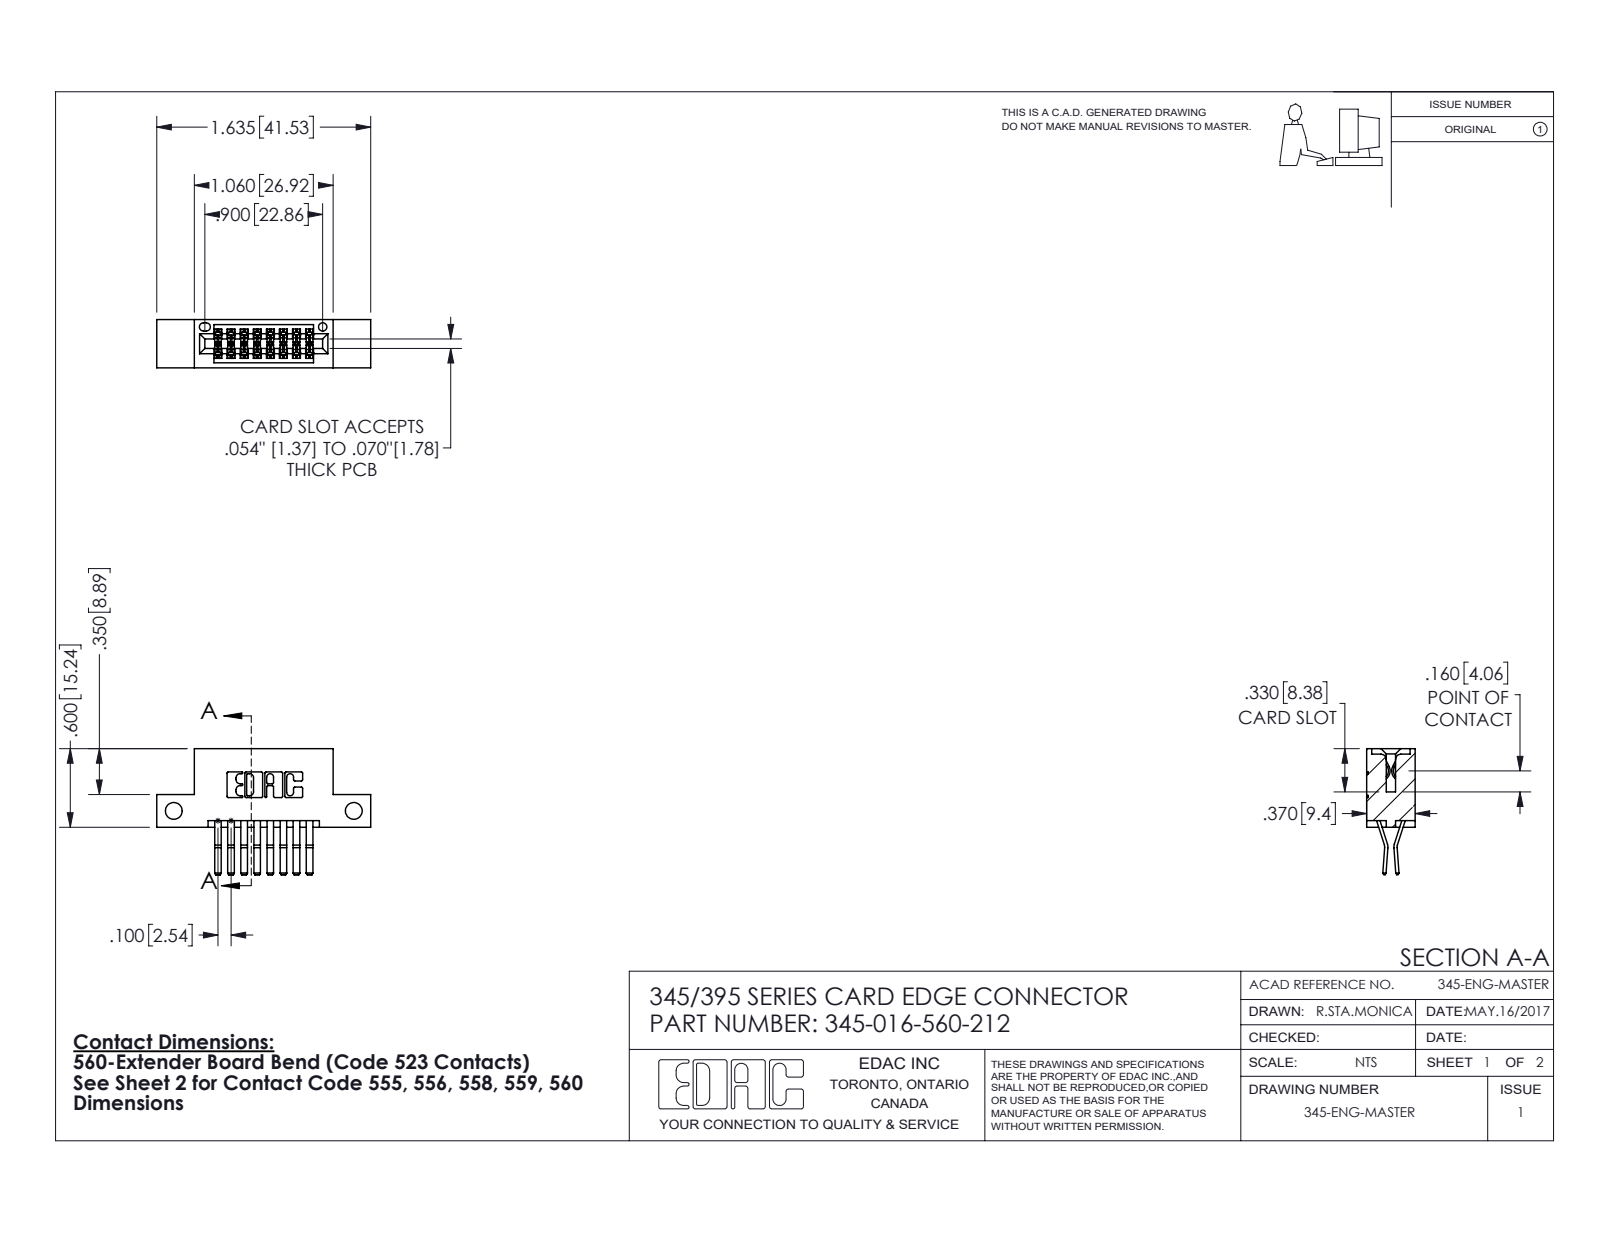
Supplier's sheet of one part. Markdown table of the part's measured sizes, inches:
| quantity | value |
| --- | --- |
| part name | 345-292-001_560 Tail; 345 Part_Flush Mounting Lugs - Side Mount; 345-016-560-212 |
| STEP written by | SolidWorks 2016 (CONFIG_CONTROL_DESIGN) |
| units | inches |
| bodies | 17 solids, 958 faces (608 planar, 350 cylindrical, 0 other) |
| overall size | 1.635 × 0.962 × 0.37 |
| volume | 0.228 in³ |
| surface area | 7.747 in² |
| round holes (diameter × count) | 0.128 × 2, 0.064 × 1 |
| partial cylindrical surfaces (radius × count) | 0.006 × 24, 0.01 × 22, 0.007 × 6, 0.031 × 6, 0.026 × 3, 0.01 × 2, 0.014 × 2, 0.019 × 2 |
| main face-to-face distances | 0.2, 0.025, 0.298, 0.072, 0.1, 0.37, 0.3, 0.098, 0.272, 0.06 |
| hole center spacings | 1.375 |
